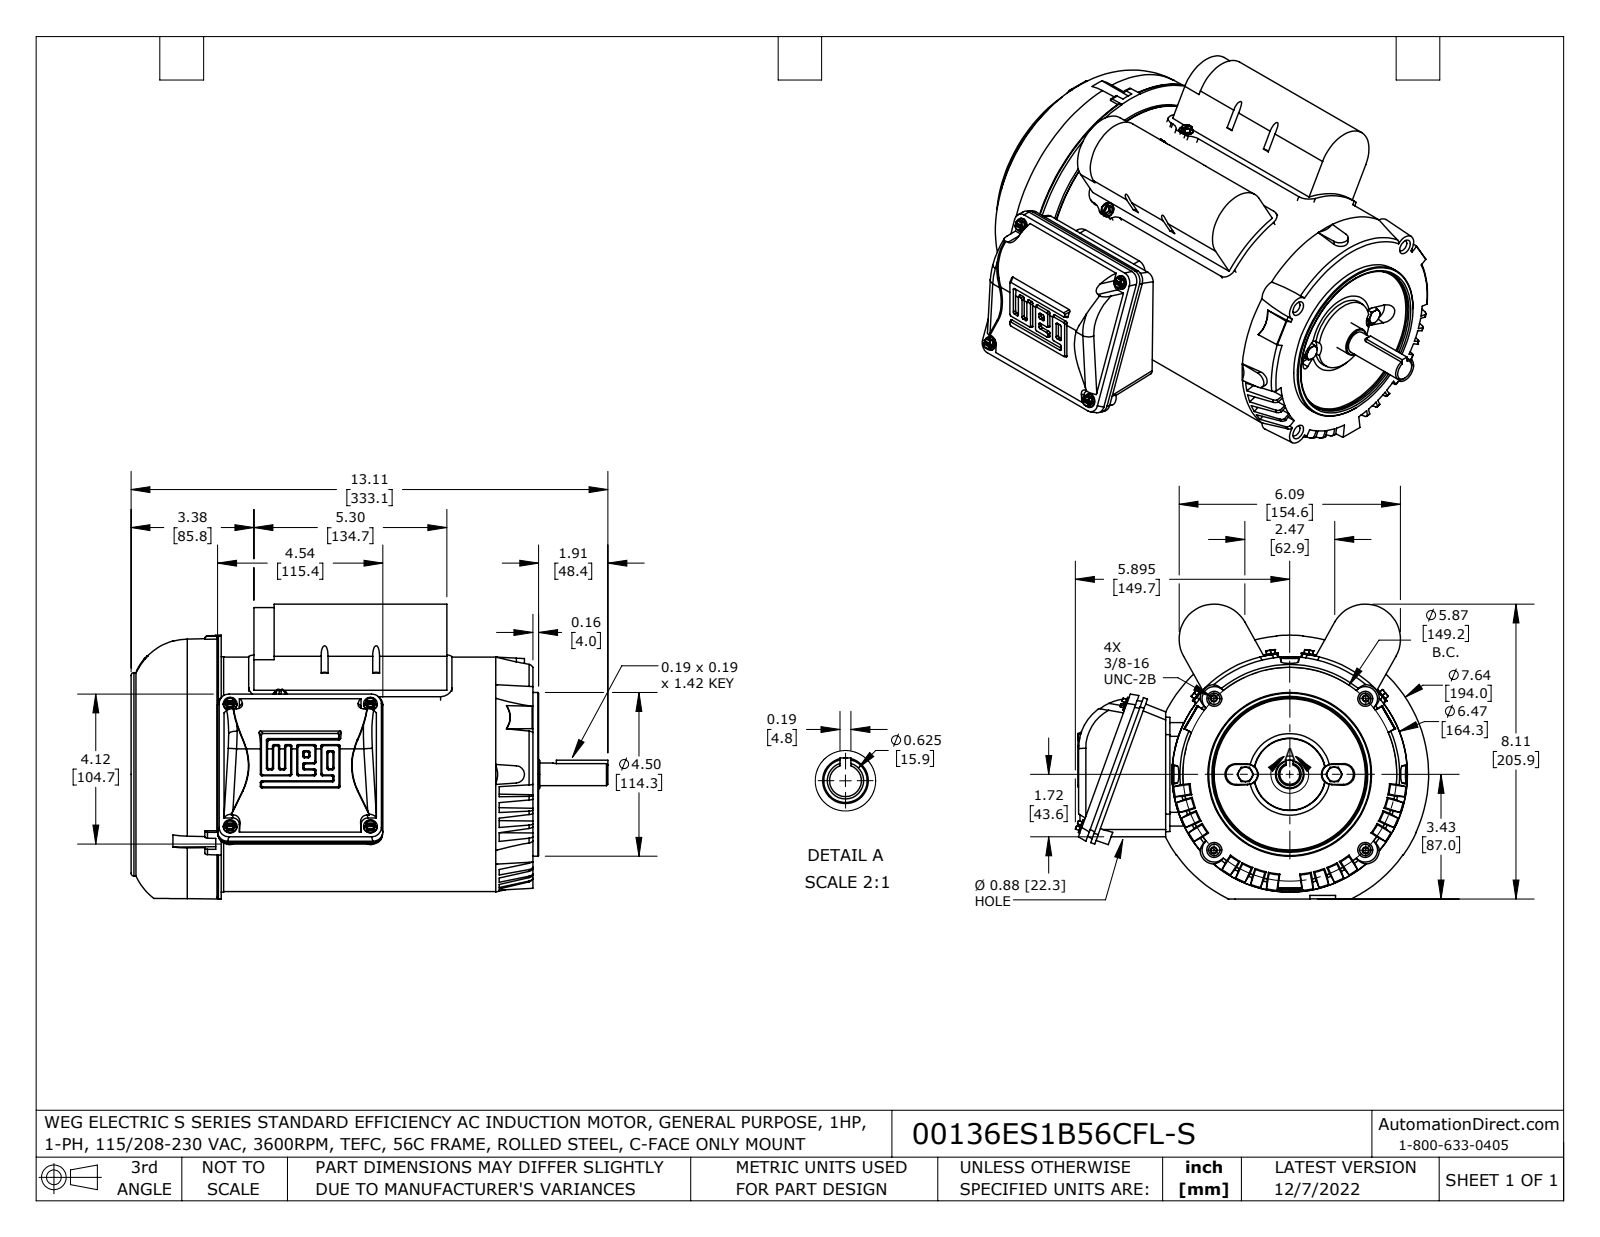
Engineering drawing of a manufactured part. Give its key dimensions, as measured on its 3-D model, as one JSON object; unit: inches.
{"part_name": "56C_1PH_TEFC_GP_13114_FL_02CAP fxt", "step_written_by": "SolidWorks 2021 (AUTOMOTIVE_DESIGN)", "units": "inches", "bodies": {"solids": 16, "faces": 1228, "planar": 475, "cylindrical": 318, "other": 435}, "overall_size": [13.114, 9.714, 8.405], "volume_in3": 446.3, "surface_area_in2": 708.8, "round_holes": [[0.313, 4], [0.157, 3]], "round_bosses_or_shafts": [[0.394, 4], [0.374, 4], [0.189, 4], [0.187, 4], [0.161, 4], [6.474, 1], [6.447, 1], [5.591, 1]], "partial_cylinders_radius": [[0.004, 48], [0.047, 38], [0.354, 9], [0.079, 8], [0.118, 8], [0.205, 8], [0.276, 8], [0.315, 8]], "face_to_face_distances": [7.48, 0.067, 7.547, 2.283, 2.35, 9.831, 10.854, 8.571, 8.504, 1.024], "hole_center_spacings": [4.154, 4.091, 0.896, 2.096, 3.258, 4.219, 4.901, 5.254]}
